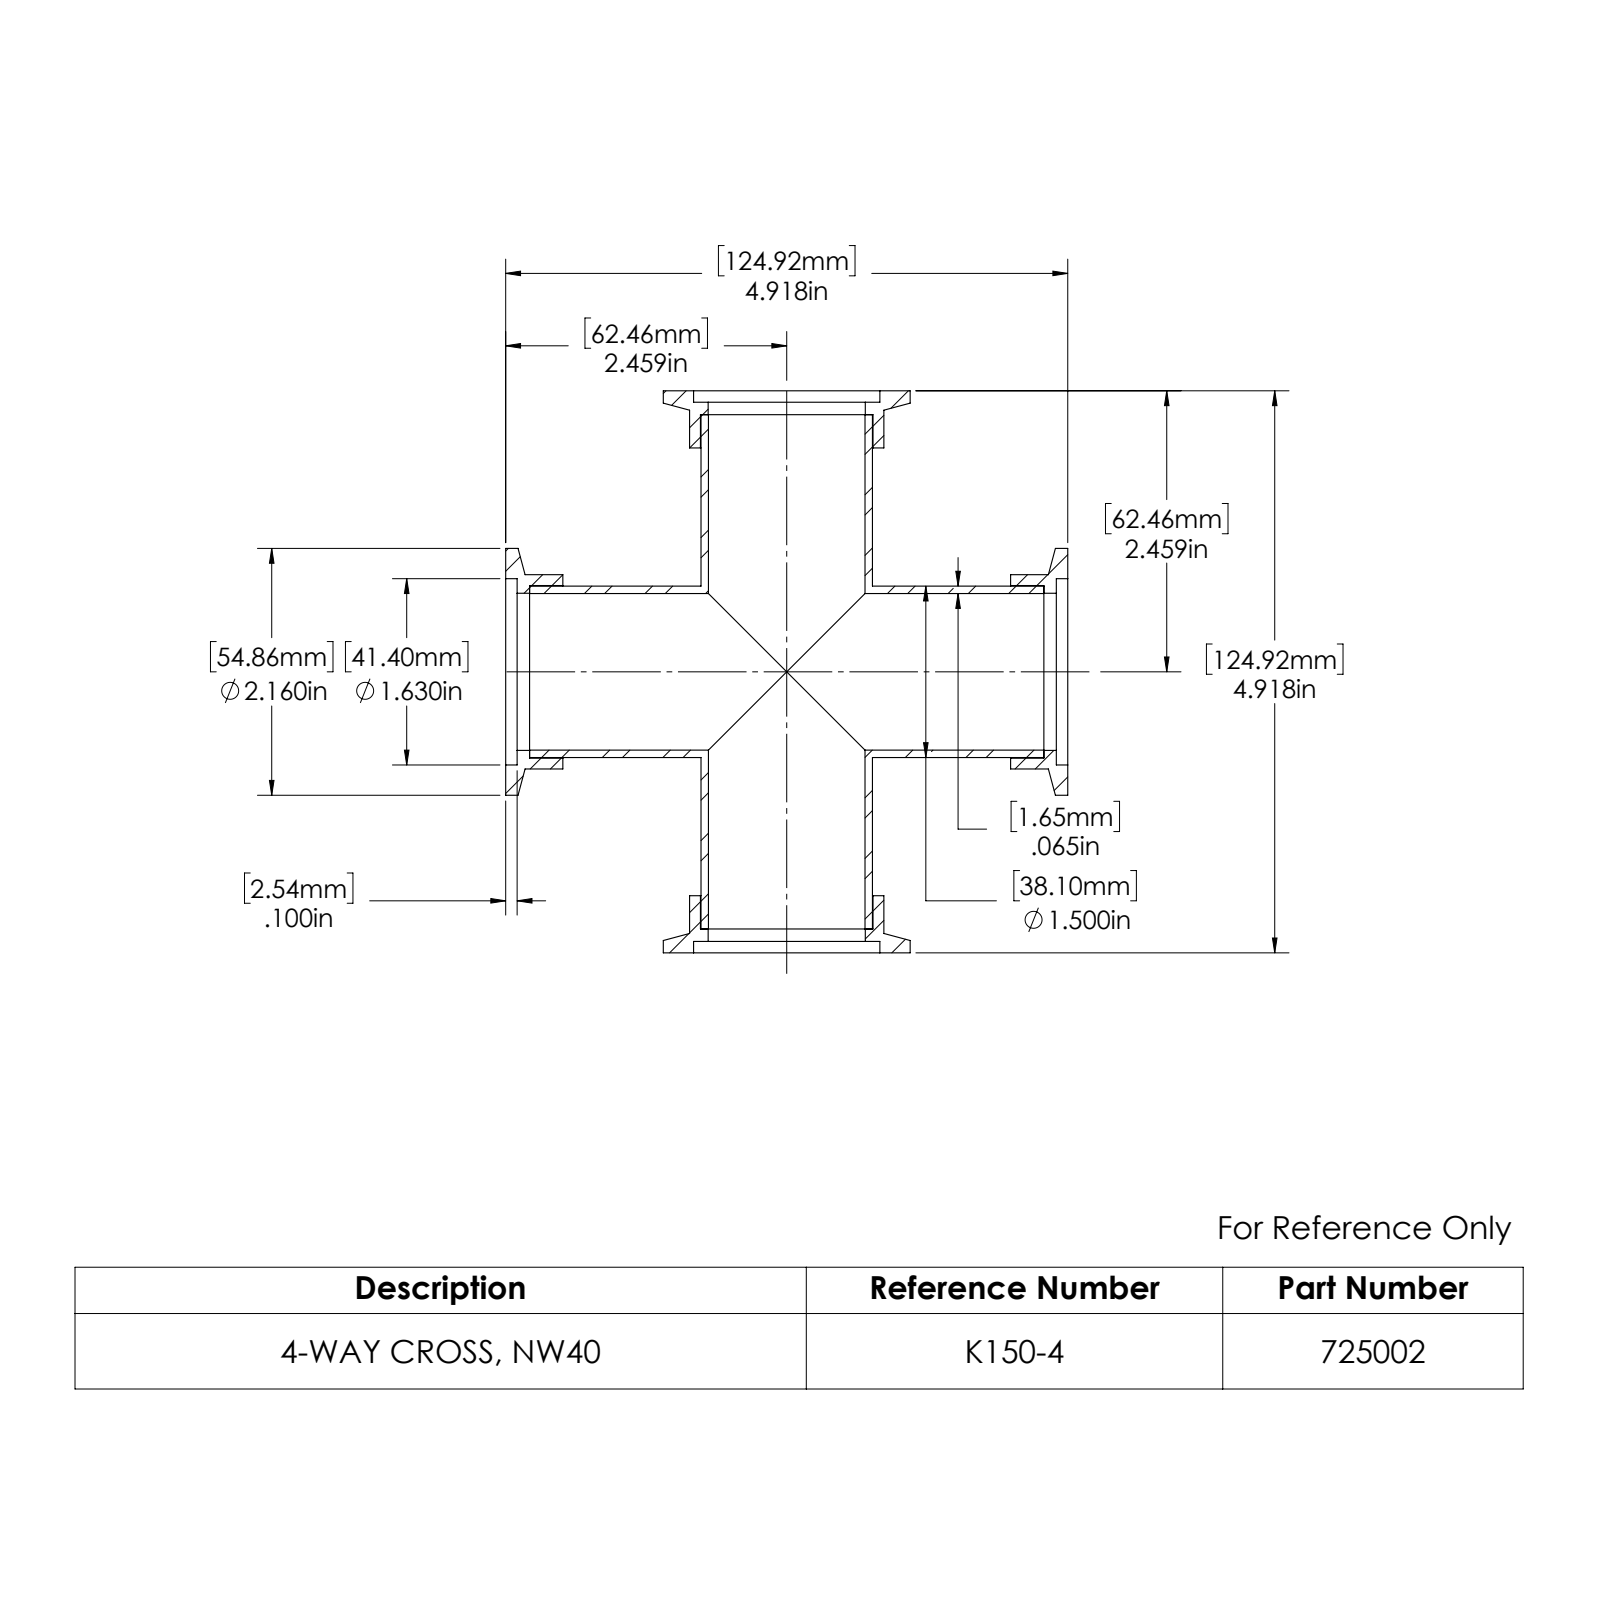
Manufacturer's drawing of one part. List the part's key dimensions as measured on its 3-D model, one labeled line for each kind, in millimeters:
Part name (STEP PRODUCT): 725002; 713003-99; 405502
STEP written by: SolidWorks 2022 (AUTOMOTIVE_DESIGN)
Units: millimetres
Bodies: 5 solids, 84 faces (20 planar, 56 cylindrical, 8 other)
Overall size (bounding box): 124.9 × 124.9 × 54.9
Volume: 62 960 mm³ · Surface area: 66 390 mm²
Round holes (diameter × count): ⌀34.8 ×2, ⌀34.9 ×2, ⌀38.4 ×2, ⌀41.4 ×2
Round bosses / shafts (diameter × count): ⌀54.9 ×2, ⌀43.2 ×2, ⌀38.1 ×2
Main face-to-face distances: 2.5, 12.7, 10.2, 117.1, 119.6, 2.8, 5.3, 124.9, 124.9, 106.9
